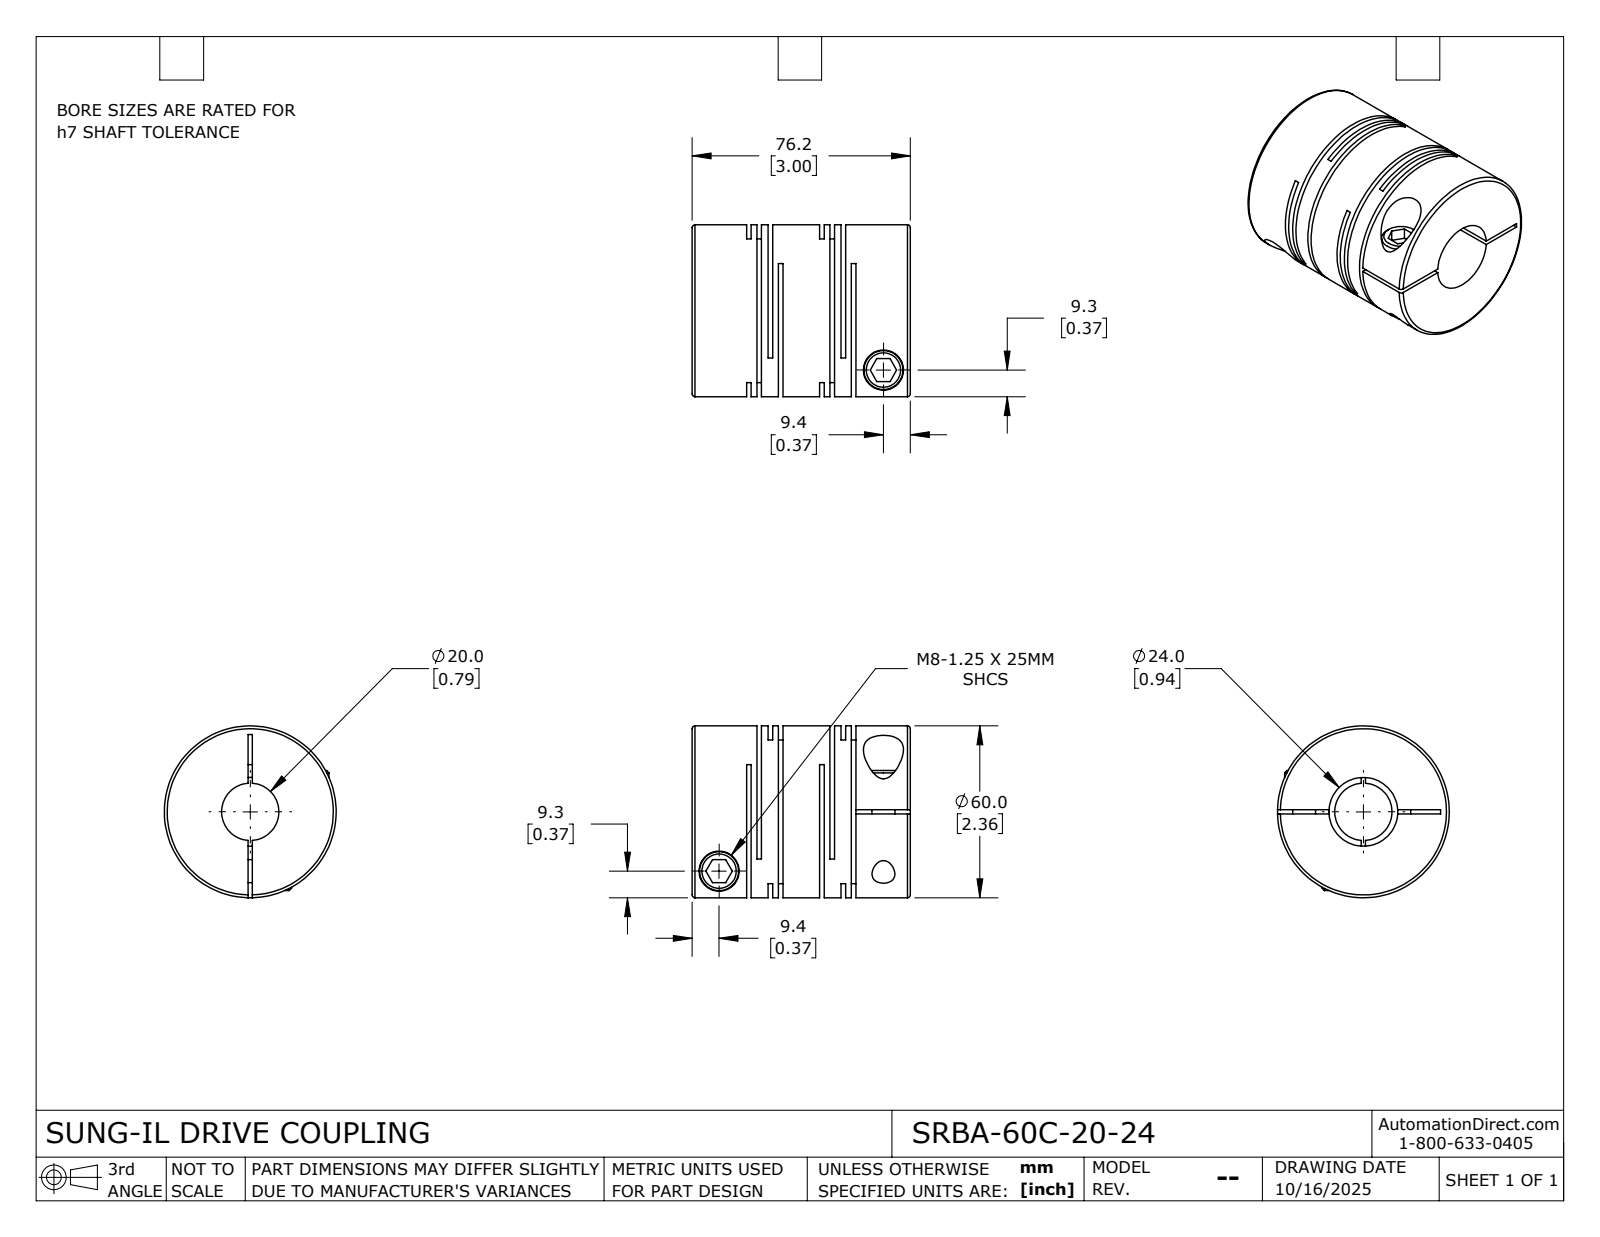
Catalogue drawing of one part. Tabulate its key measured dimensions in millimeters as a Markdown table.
| quantity | value |
| --- | --- |
| part name | SRBA-60C-20-24 |
| STEP written by | SolidWorks 2024 (CONFIG_CONTROL_DESIGN) |
| units | millimeters |
| bodies | 1 solid, 115 faces (60 planar, 42 cylindrical, 13 other) |
| overall size | 76.2 × 60 × 60 |
| volume | 154 255 mm³ |
| surface area | 57 327 mm² |
| round holes (diameter × count) | 8 × 2, 14 × 2, 20 × 1, 24 × 1 |
| round bosses / shafts (diameter × count) | 13.6 × 2, 60 × 1 |
| main face-to-face distances | 1.6, 3.6, 7.5, 25.5, 33, 27.1, 2, 5.9, 23.9, 3.9 |
